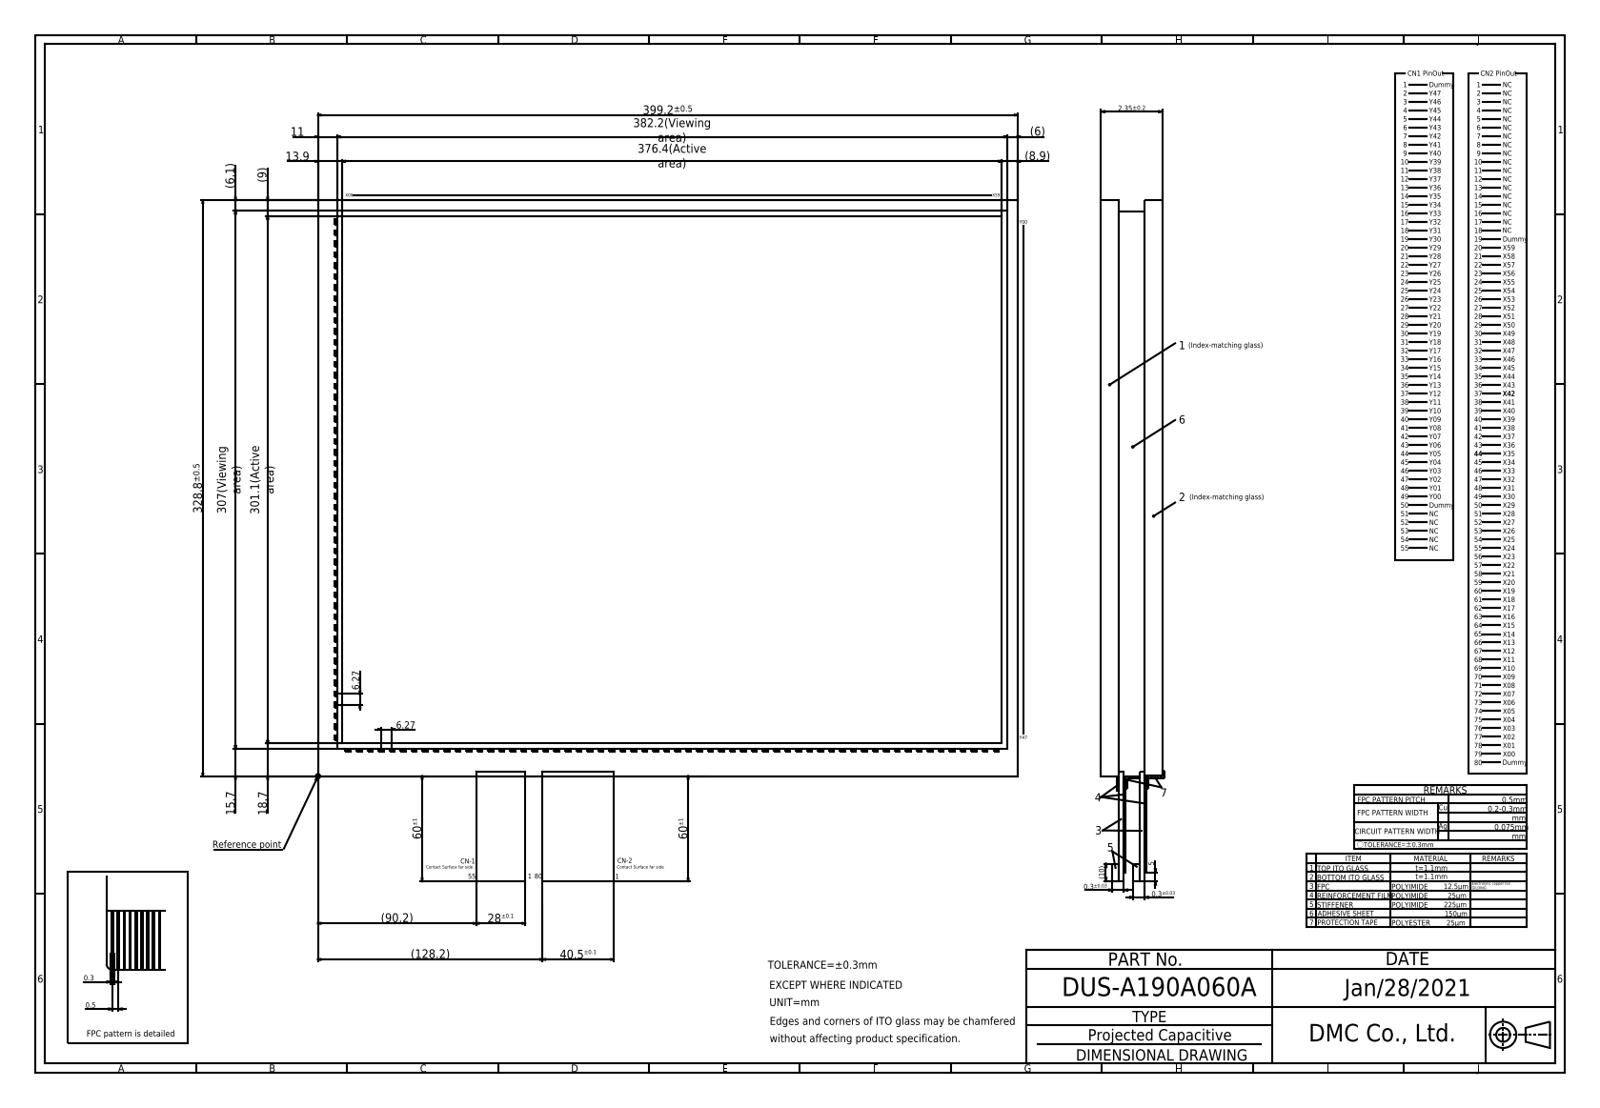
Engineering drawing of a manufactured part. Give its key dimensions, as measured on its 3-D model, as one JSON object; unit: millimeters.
{"part_name": "DUS-A190A060A", "step_written_by": "Autodesk Inventor 2020 (CONFIG_CONTROL_DESIGN)", "units": "millimeters", "bodies": {"solids": 1, "faces": 578, "planar": 574, "cylindrical": 4, "other": 0}, "overall_size": [558.88, 460.32, 2.35], "volume_mm3": 308635, "surface_area_mm2": 274517, "partial_cylinders_radius": [[0.2, 4]], "face_to_face_distances": [2.35, 1.1, 2.25, 1.2, 1.15, 1, 1.25, 328.8, 399.2, 0.8]}
